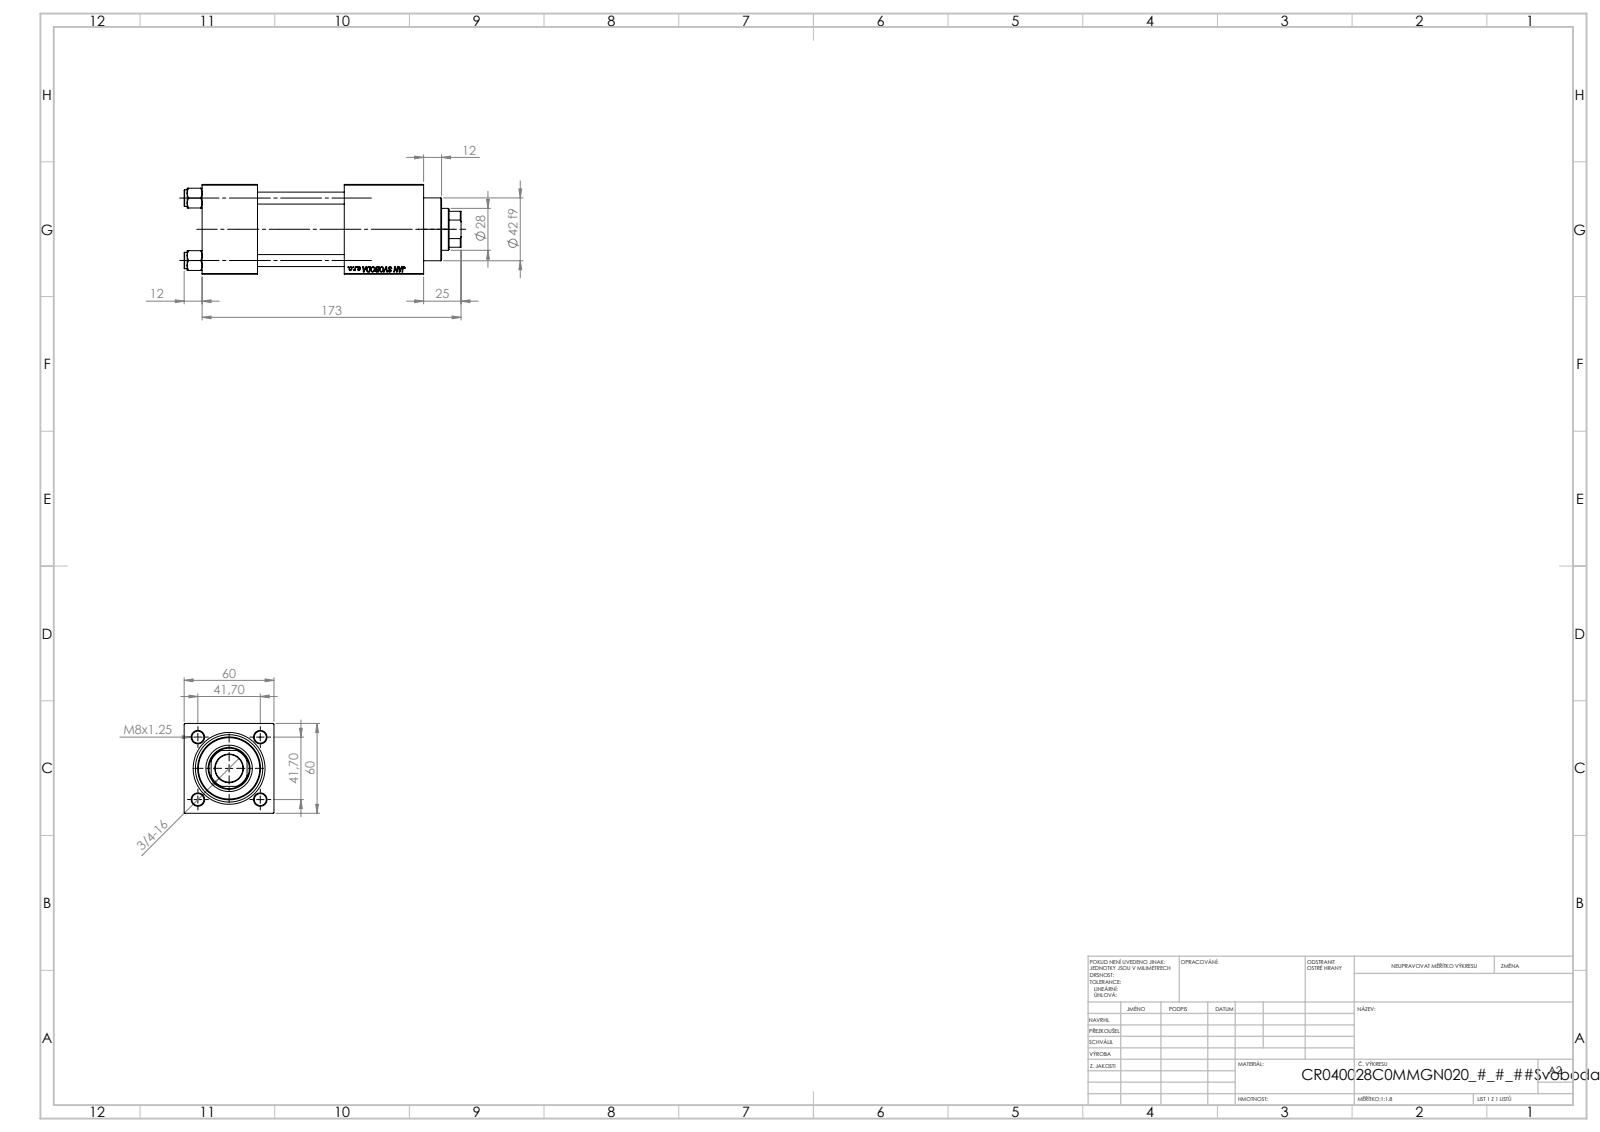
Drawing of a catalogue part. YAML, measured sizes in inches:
part_name: "V215CR_C_Body; V215CR_VCP_C; V215CR_C_TYCINKA; V215_VC_A (+1 more)"
step_written_by: "SolidWorks 2019 (CONFIG_CONTROL_DESIGN)"
units: inches
bodies: {solids: 11, faces: 1148, planar: 526, cylindrical: 86, other: 536}
overall_size: [7.283, 2.362, 2.362]
volume: 25.9
surface_area: 172.6
round_holes:
  - {diameter: 0.315, count: 4}
  - {diameter: 0.276, count: 2}
  - {diameter: 0.656, count: 2}
  - {diameter: 0.945, count: 2}
  - {diameter: 0.728, count: 1}
  - {diameter: 1.102, count: 1}
  - {diameter: 1.22, count: 1}
  - {diameter: 1.575, count: 1}
  - {diameter: 1.772, count: 1}
round_bosses_or_shafts:
  - {diameter: 0.433, count: 4}
  - {diameter: 1.811, count: 1}
  - {diameter: 1.654, count: 1}
partial_cylinders:
  - {radius: 0.531, count: 1}
face_to_face_distances: [2.362, 1.457, 2.283, 3.74, 2.087, 4.697, 3.24, 0.957, 5.827, 4.37]
hole_center_spacings: [1.161, 1.642, 2.322, 3.642]
